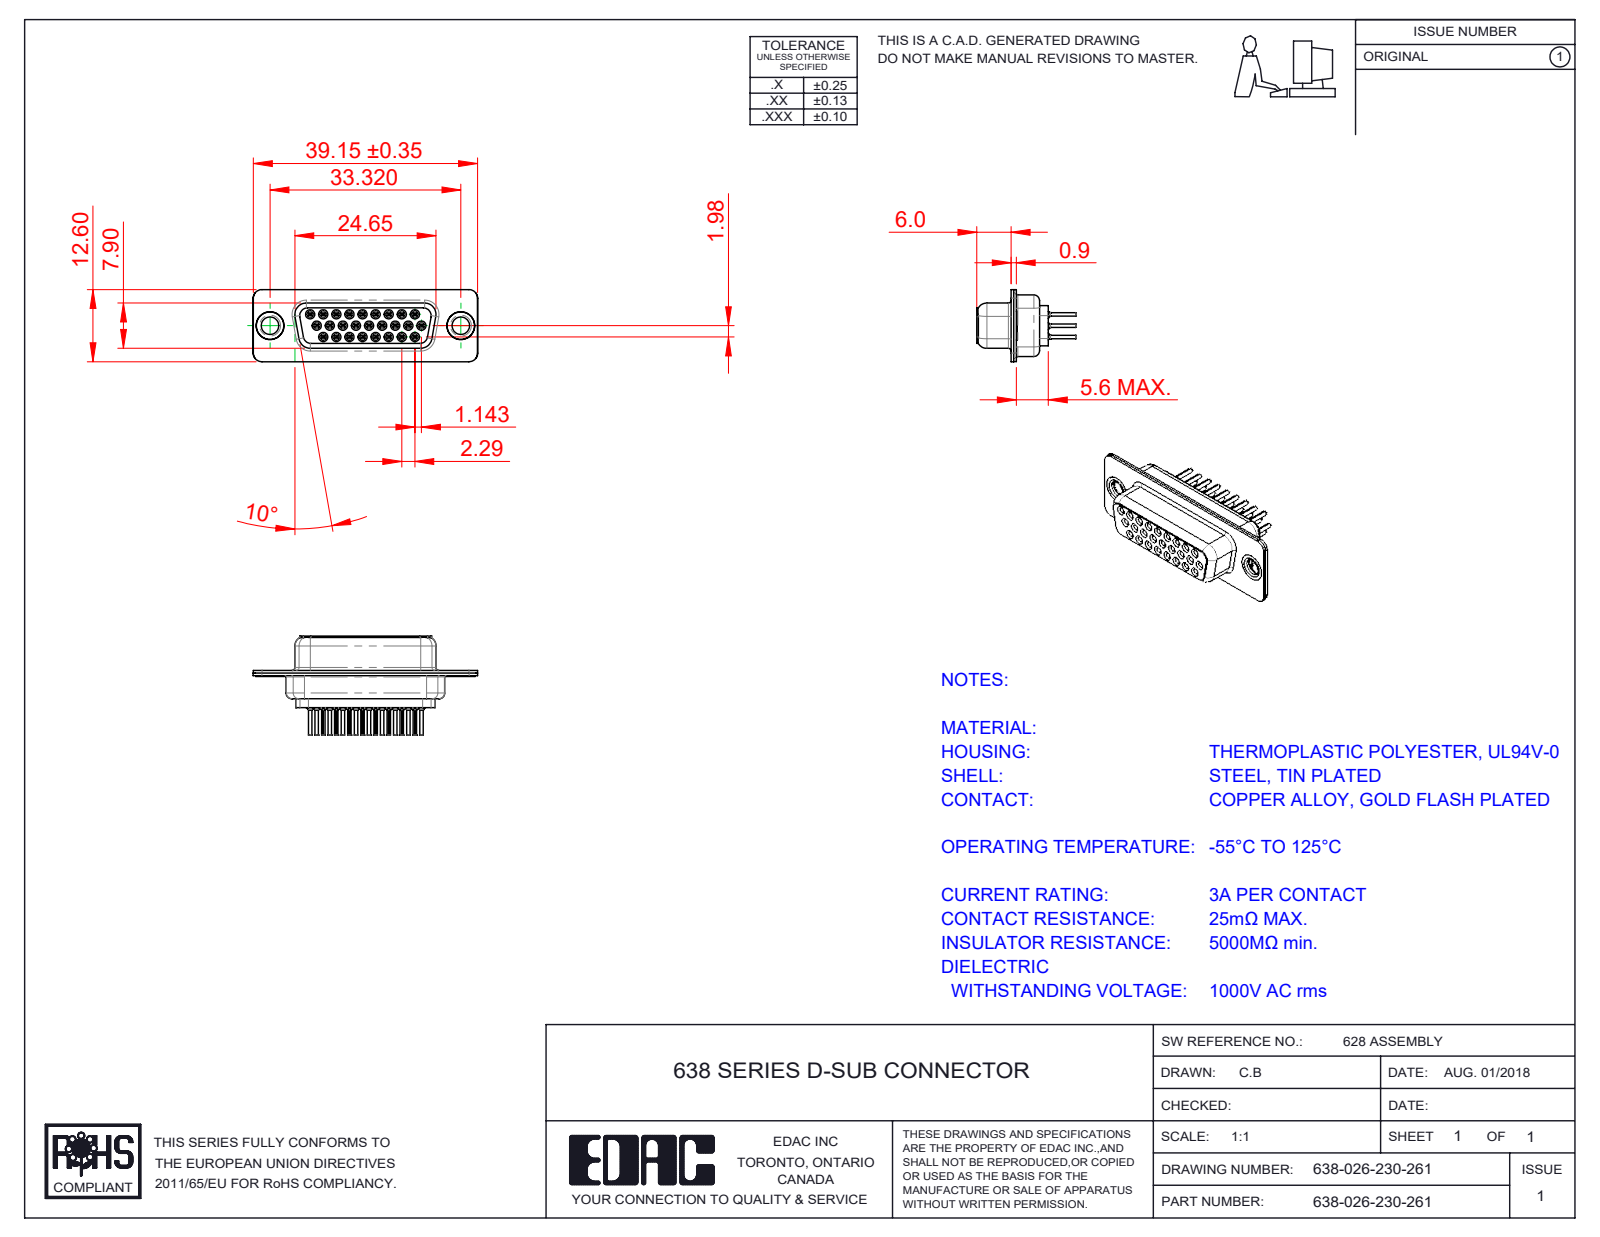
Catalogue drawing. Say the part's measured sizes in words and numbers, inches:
The part is named "638 Shell Rear_26 Contacts; 638 Contact Row 1_30; 638 Contact Row 2_30; 638 Thru Hole Rivet (+4 more)". Its 3-D file was written by "SolidWorks 2020 (CONFIG_CONTROL_DESIGN)". It is 31 solids with 3555 faces: 873 planar, 979 cylindrical and 1703 other. Overall it measures 1.543 by 0.681 by 0.496 inches. Its volume is 0.13 cubic inches and its surface area 12.65 square inches. Round holes: 26 of diameter 0.008, 26 of diameter 0.031, 26 of diameter 0.039, 26 of diameter 0.043, 26 of diameter 0.063, 26 of diameter 0.067, 26 of diameter 0.071, 2 of diameter 0.12, 2 of diameter 0.157, 2 of diameter 0.159, 2 of diameter 0.191. Round bosses or shafts: 26 of diameter 0.079, 26 of diameter 0.059, 26 of diameter 0.047, 26 of diameter 0.024, 2 of diameter 0.197, 2 of diameter 0.195, 2 of diameter 0.189, 2 of diameter 0.14. Partial cylindrical surfaces (rounded edges, fillets, slot ends): 52 of radius 0.004, 20 of radius 0.059, 18 of radius 0.011, 12 of radius 0.079, 8 of radius 0.061, 5 of radius 0.053, 4 of radius 0.01, 4 of radius 0.02. The main face-to-face distances are 0.018, 0.016, 0.056, 0.35, 0.035, 0.26, 0.09, 0.055, 0.278, 0.033. The hole center spacings are 0.156, 0.09, 0.18, 0.238, 0.09, 0.324, 0.27, 0.413.
